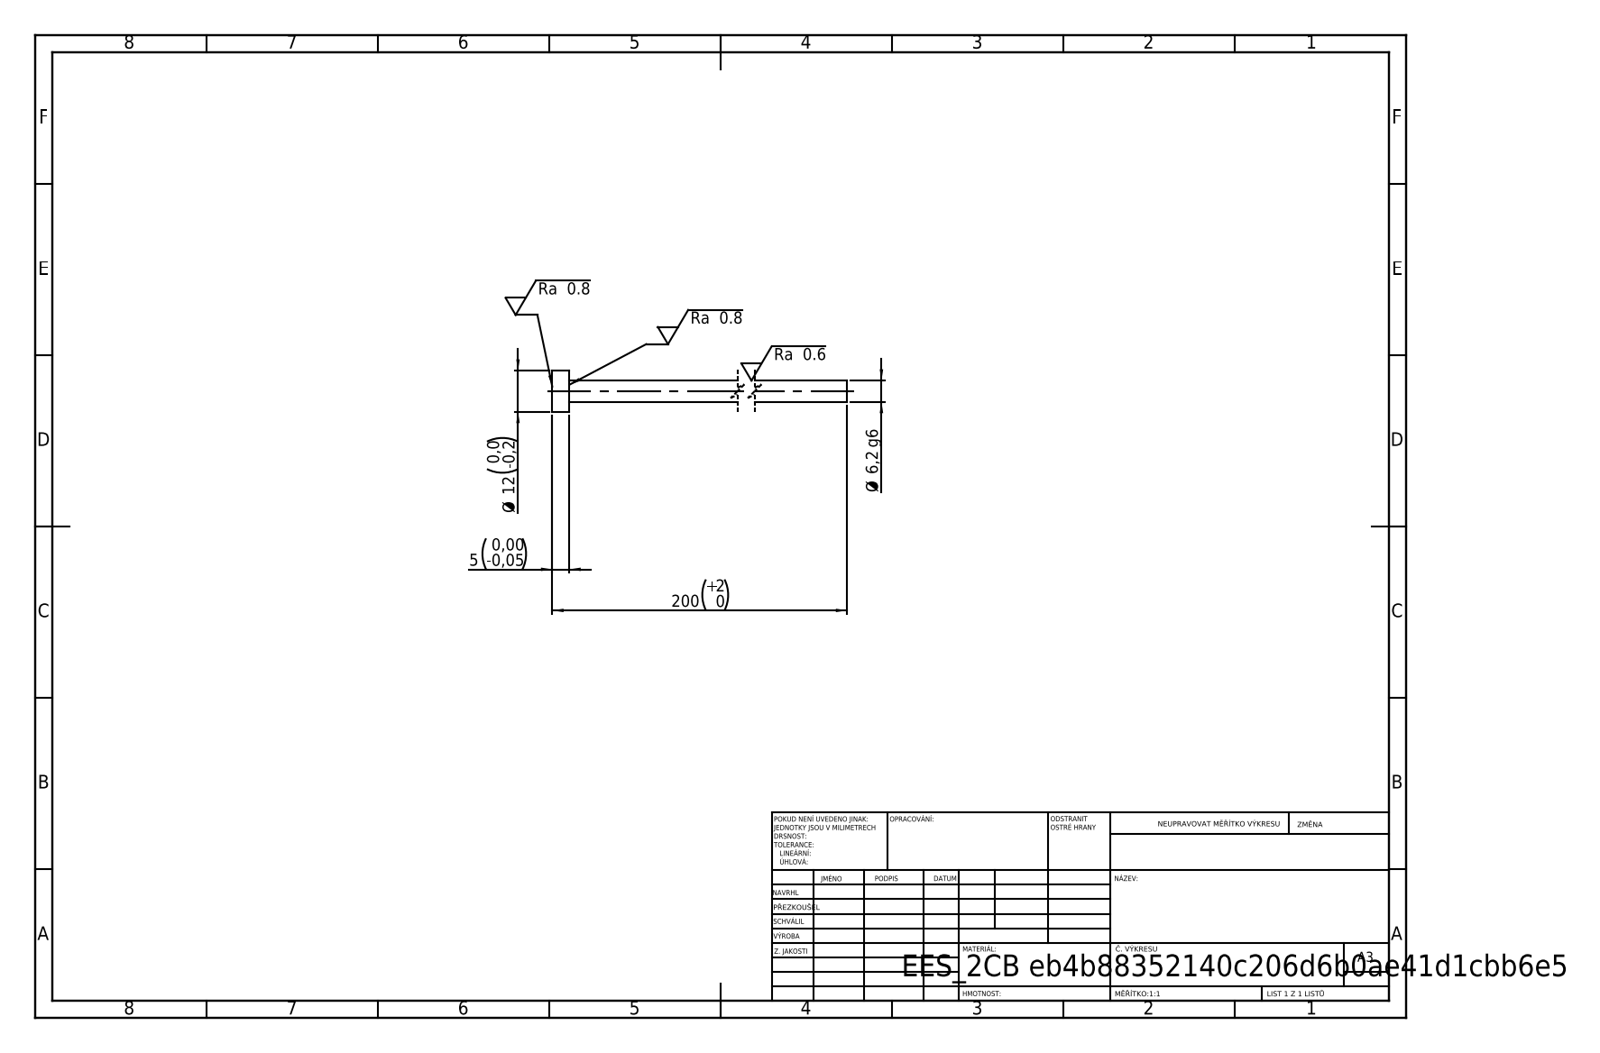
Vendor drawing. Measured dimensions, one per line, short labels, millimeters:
written by: SolidWorks 2019 (CONFIG_CONTROL_DESIGN)
unit: mm
bodies: 1 solid, 7 faces (3 planar, 4 cylindrical, 0 other)
size: 200 × 12 × 12
volume: 6 453 mm³; area: 4 213 mm²
bosses: 1× ⌀12, 1× ⌀6.2
face distances: 5, 200, 195
